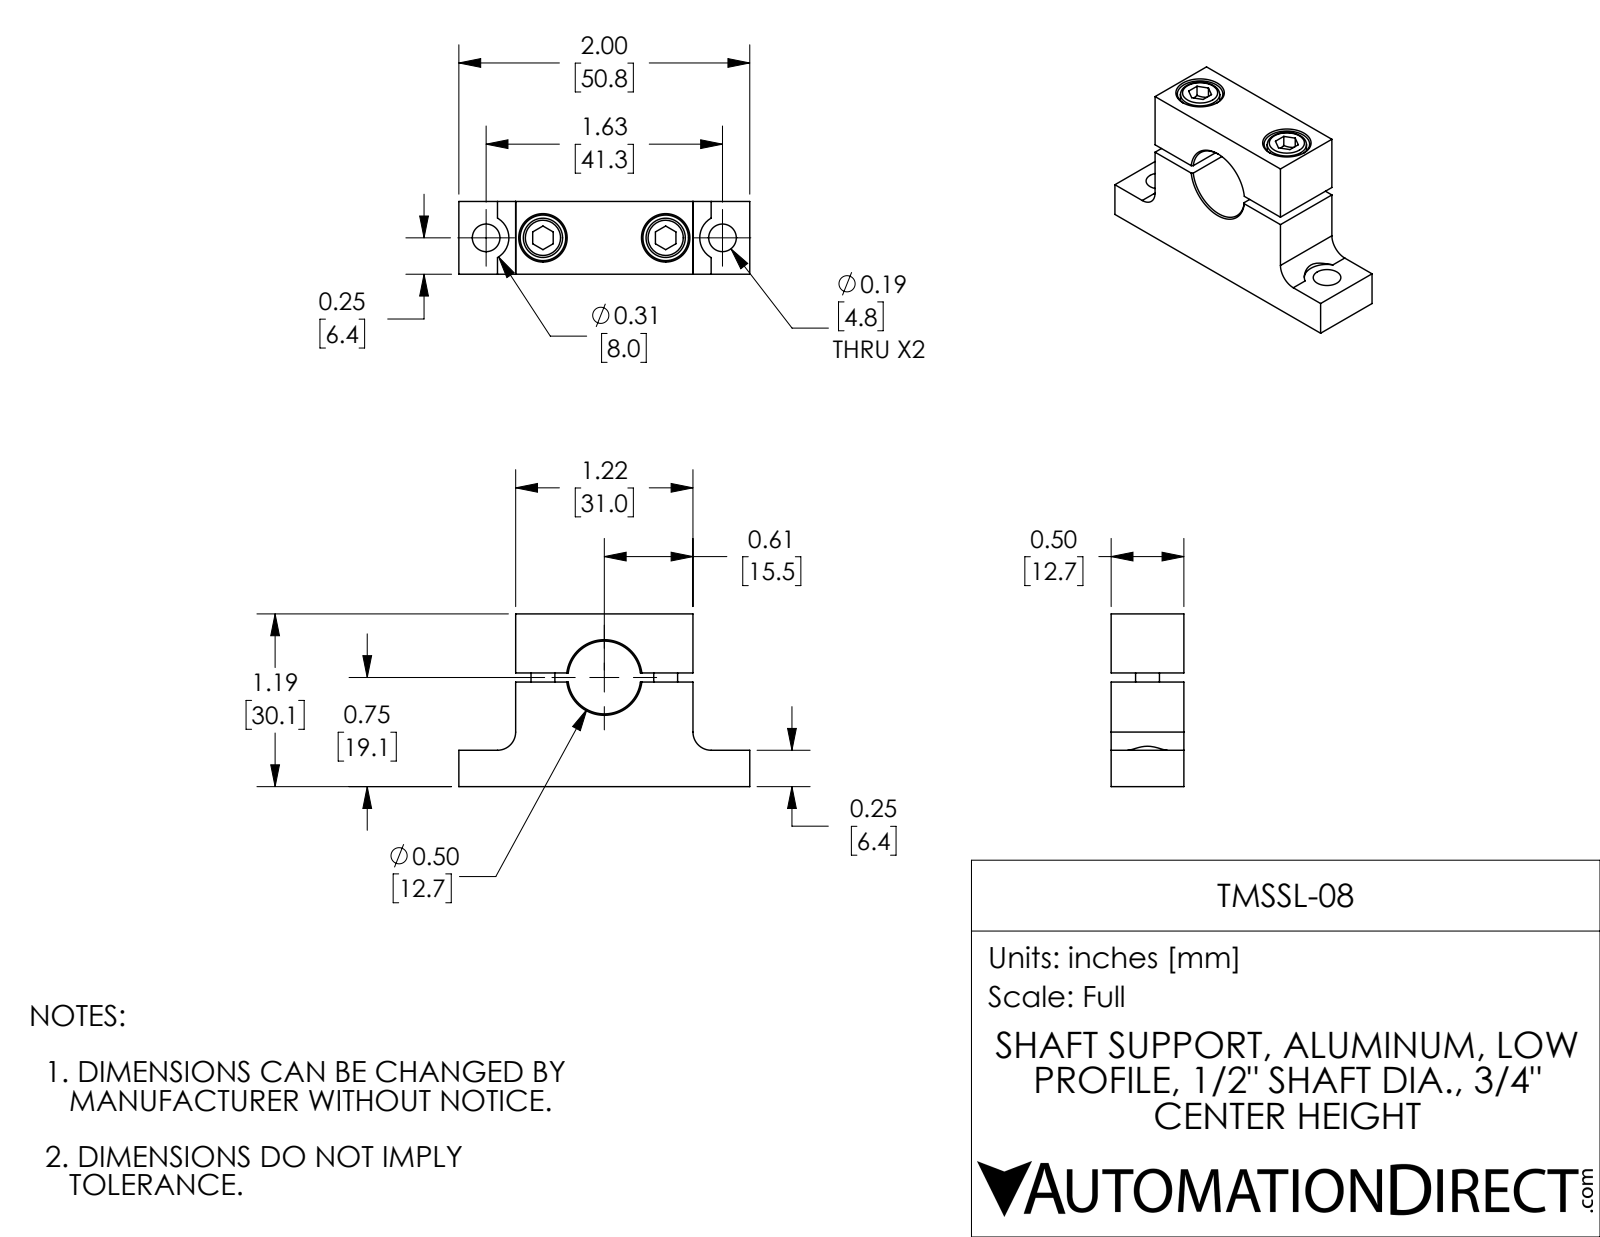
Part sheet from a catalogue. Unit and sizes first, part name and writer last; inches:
Units: inches
Overall size (bounding box): 2 × 1.187 × 0.5
Round holes (diameter × count): ⌀0.13 ×2, ⌀0.177 ×2, ⌀0.19 ×2, ⌀0.313 ×2, ⌀0.5 ×1
Round bosses / shafts (diameter × count): ⌀0.27 ×2, ⌀0.164 ×2
Partial cylindrical surfaces — rounded edges, fillets, slot ends (radius × count): R0.125 ×2, R0.156 ×2
Main face-to-face distances: 0.5, 1.187, 1.219, 0.719, 0.468, 0.781, 0.062, 0.406, 0.391, 1.609
Hole centre spacings: 0.391, 1.235, 0.844, 1.625
Volume: 0.675 in³ · Surface area: 9.733 in²
Bodies: 4 solids, 94 faces (38 planar, 31 cylindrical, 25 other)
Part name (STEP PRODUCT): TMSSL-08
STEP written by: SolidWorks 2017 (AUTOMOTIVE_DESIGN)
